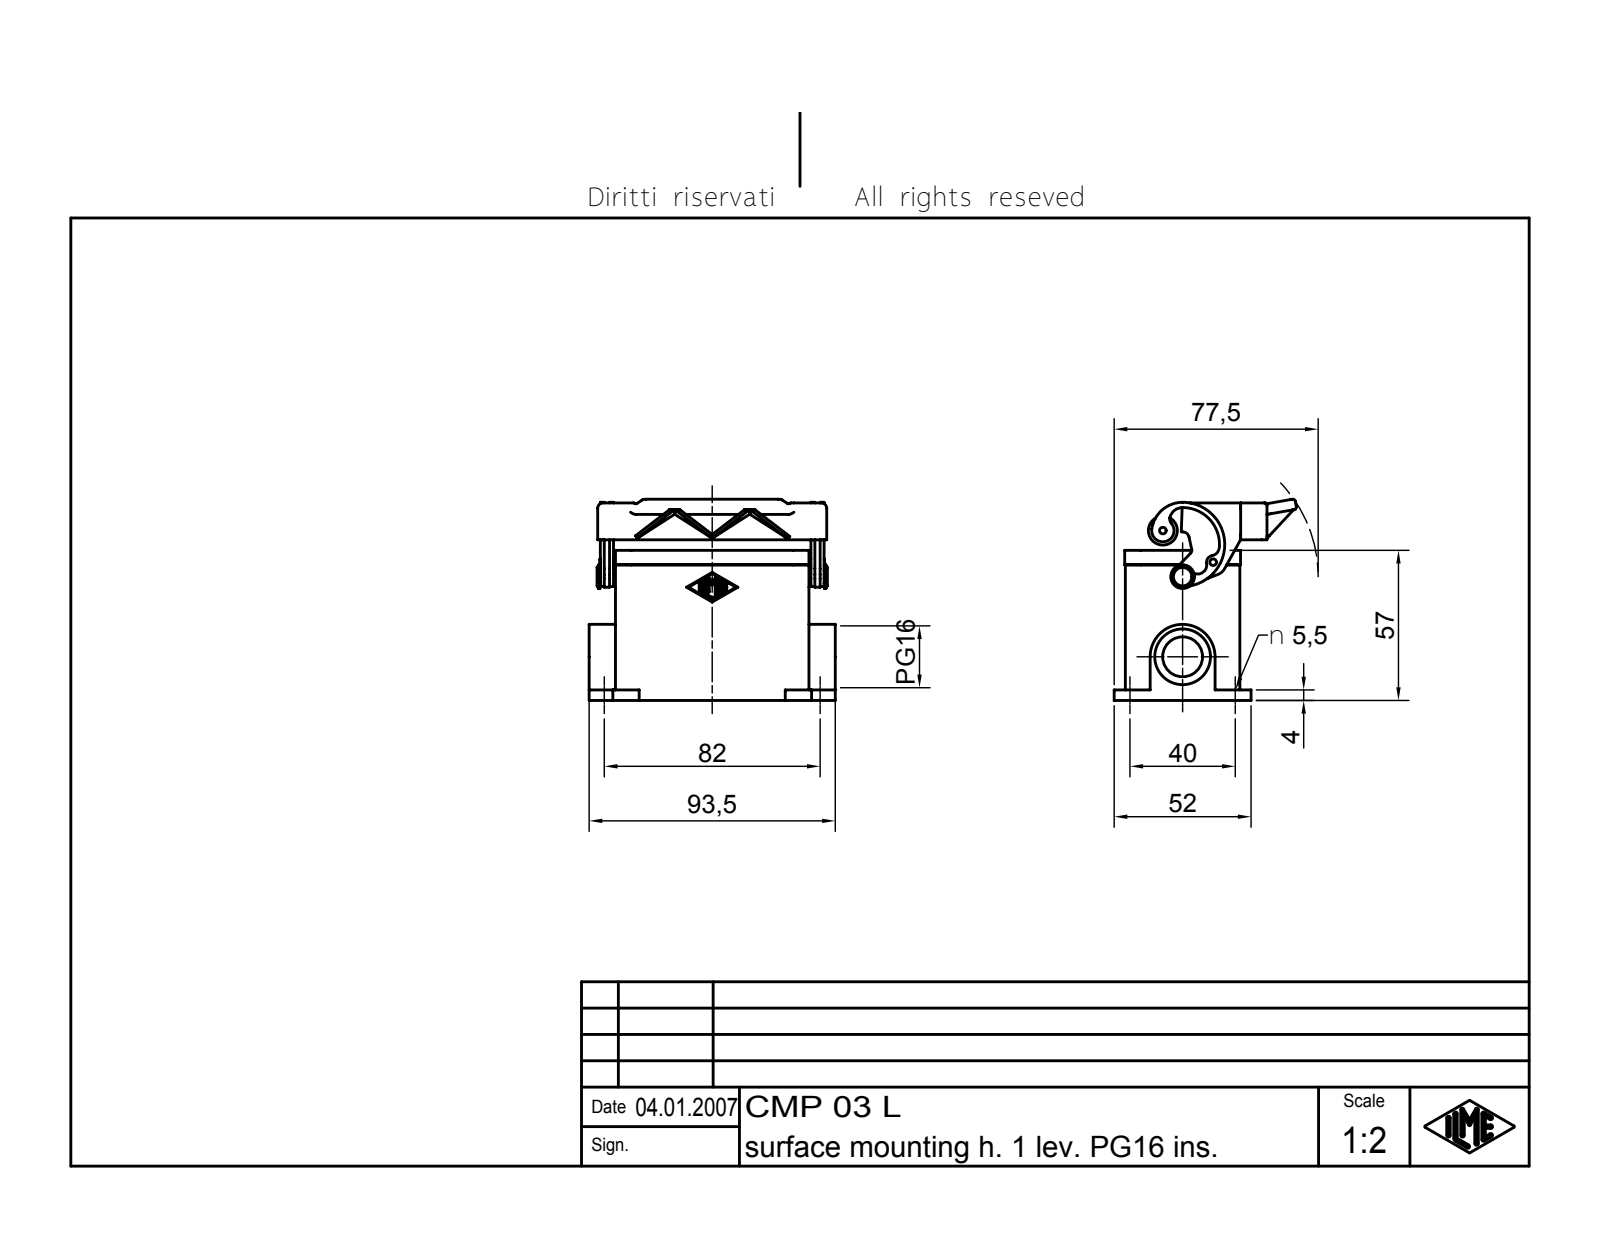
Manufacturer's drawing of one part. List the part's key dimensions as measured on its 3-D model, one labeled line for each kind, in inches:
Part name (STEP PRODUCT): CMP 03 L
STEP written by: Autodesk Inventor 7 (AUTOMOTIVE_DESIGN)
Units: inches
Bodies: 4 solids, 432 faces (164 planar, 123 cylindrical, 145 other)
Overall size (bounding box): 3.681 × 3.009 × 2.724
Volume: 5.212 in³ · Surface area: 72.61 in²
Round holes (diameter × count): ⌀0.217 ×4, ⌀0.079 ×1, ⌀0.597 ×1, ⌀0.833 ×1
Round bosses / shafts (diameter × count): ⌀0.433 ×1, ⌀0.354 ×1, ⌀0.197 ×1, ⌀0.118 ×1, ⌀0.098 ×1
Partial cylindrical surfaces — rounded edges, fillets, slot ends (radius × count): R0.015 ×14, R0.079 ×12, R0.236 ×8, R0.039 ×7, R0.059 ×5, R0.118 ×4, R0.098 ×3, R0.138 ×2
Main face-to-face distances: 0.118, 1.594, 0.157, 1.713, 1.476, 0.463, 0.344, 2.431, 2.028, 1.87
Hole centre spacings: 1.575, 3.228, 3.592, 1.486
